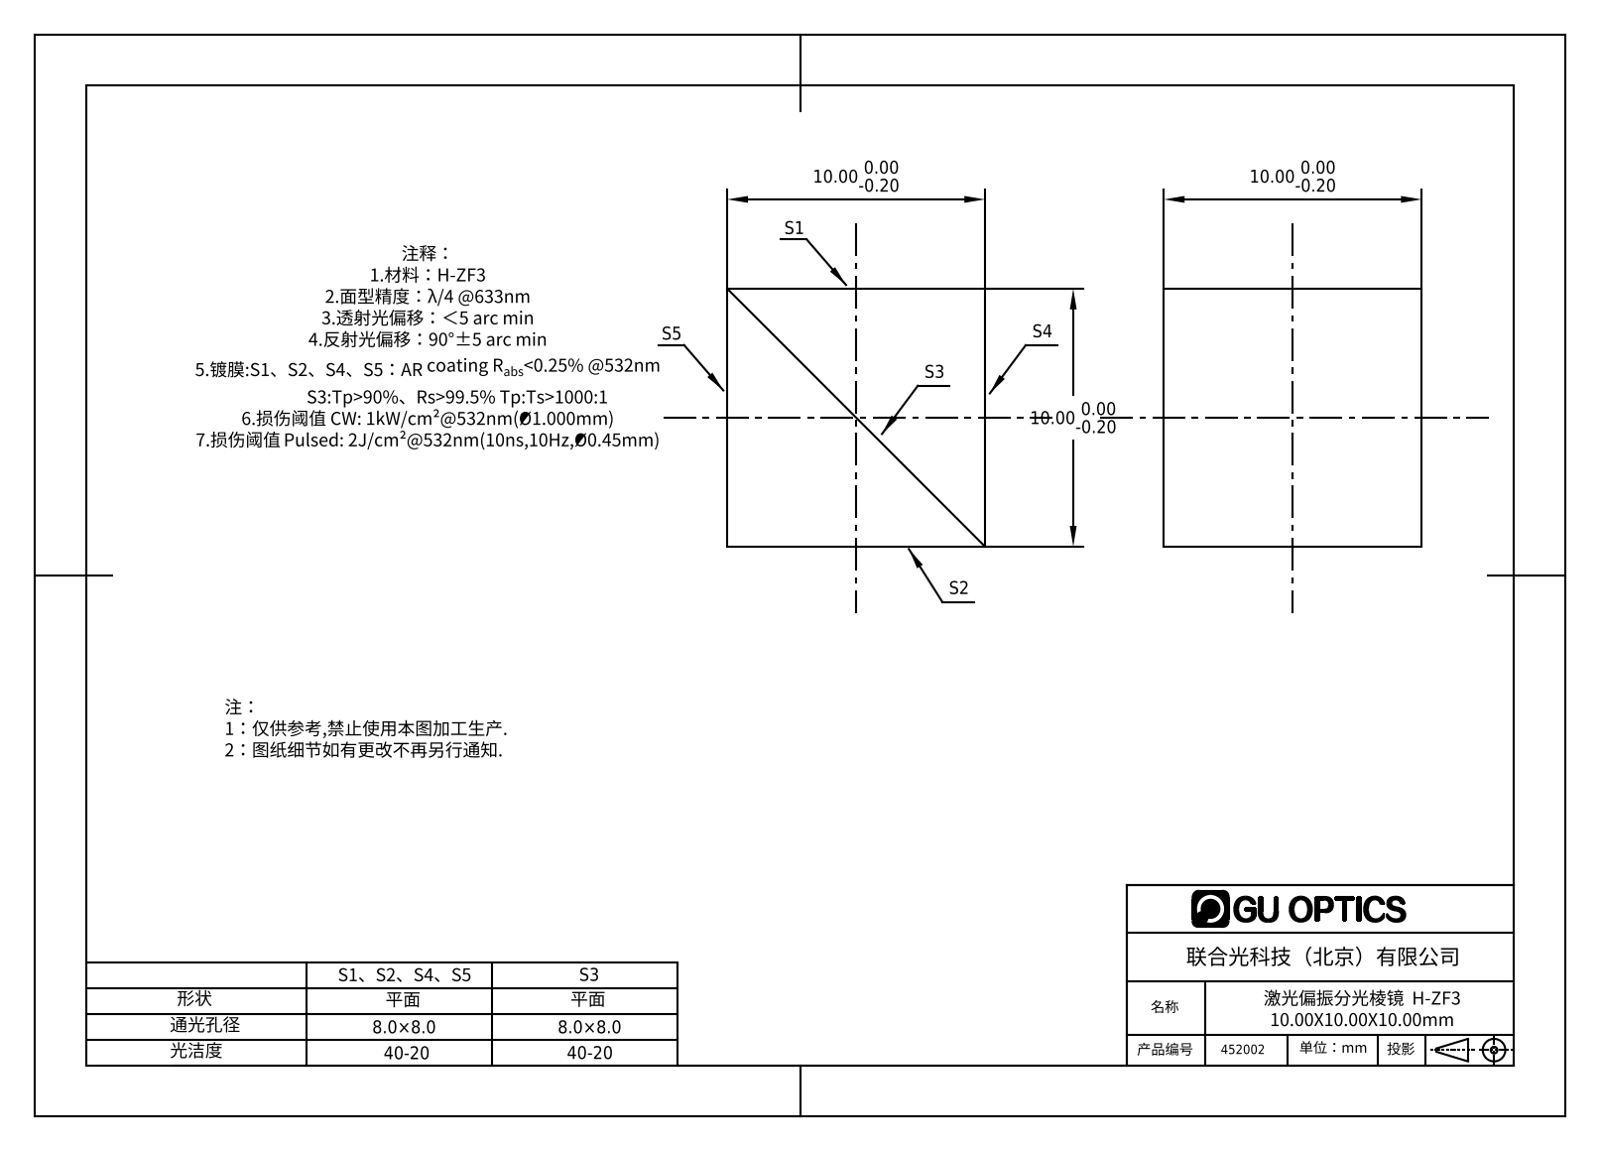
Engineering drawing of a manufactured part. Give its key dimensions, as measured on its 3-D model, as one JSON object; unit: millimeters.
{"part_name": "452000", "step_written_by": "SolidWorks 2016 (AUTOMOTIVE_DESIGN)", "units": "millimeters", "bodies": {"solids": 2, "faces": 10, "planar": 10, "cylindrical": 0, "other": 0}, "overall_size": [10, 10, 10], "volume_mm3": 1000, "surface_area_mm2": 883, "face_to_face_distances": [10]}
